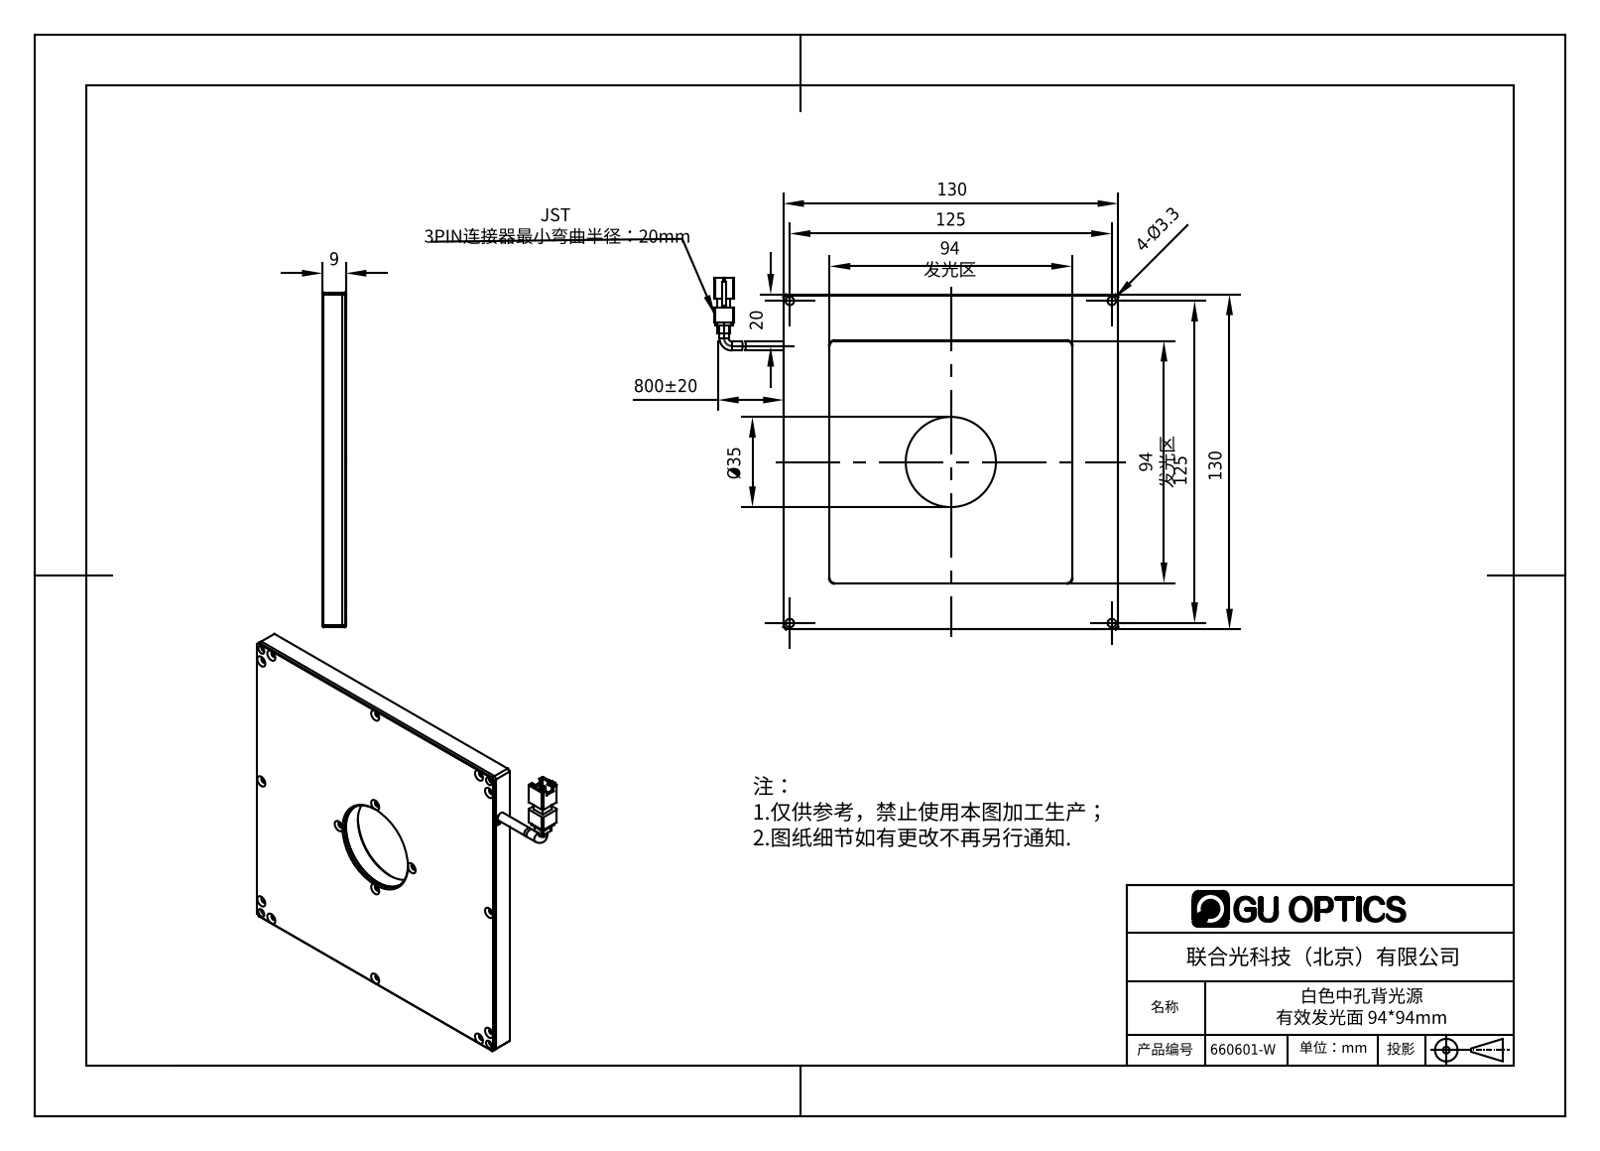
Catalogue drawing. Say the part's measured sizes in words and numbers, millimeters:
The part is named "660601-W". Its 3-D file was written by "SolidWorks 2016 (AUTOMOTIVE_DESIGN)". It is 6 solids with 474 faces: 191 planar, 148 cylindrical and 135 other. Overall it measures 157 by 136.5 by 10 millimeters. Its volume is 93 254 cubic millimeters and its surface area 85 777 square millimeters. Round holes: 16 of diameter 1.6, 12 of diameter 2, 12 of diameter 2.2, 4 of diameter 2.4, 4 of diameter 3.3, 1 of diameter 35, 1 of diameter 43. Round bosses or shafts: 2 of diameter 3.5, 1 of diameter 45.8, 1 of diameter 42.8. Partial cylindrical surfaces (rounded edges, fillets, slot ends): 8 of radius 0.5, 6 of radius 1.5, 4 of radius 1, 4 of radius 2, 1 of radius 1.6. The main face-to-face distances are 4, 6.5, 1.5, 8, 2.5, 9, 5, 1, 7.5, 126. The hole center spacings are 62.5, 125, 5.5, 57, 62.74, 65.62, 71.1, 72.63.
